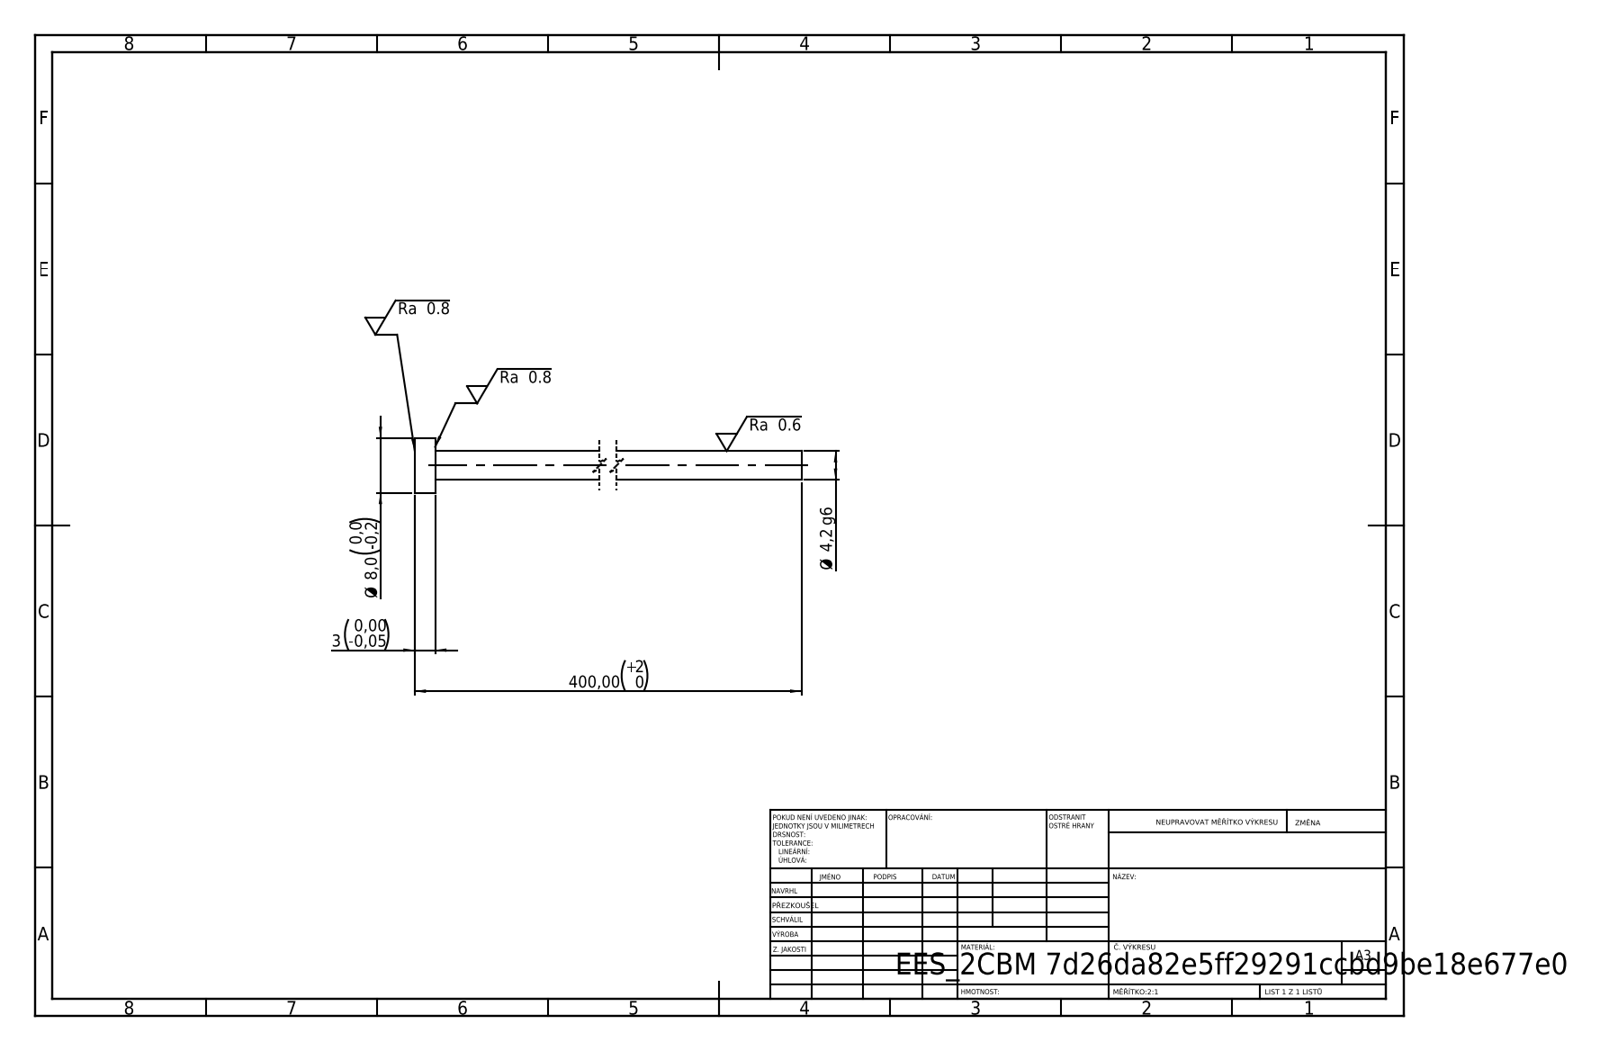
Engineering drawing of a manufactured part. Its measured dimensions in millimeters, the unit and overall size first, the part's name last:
Units: millimetres
Overall size (bounding box): 400 × 8 × 8
Round bosses / shafts (diameter × count): ⌀8 ×1, ⌀4.2 ×1
Main face-to-face distances: 3, 400, 397
Volume: 5 651 mm³ · Surface area: 5 414 mm²
Bodies: 1 solid, 7 faces (3 planar, 4 cylindrical, 0 other)
STEP written by: SolidWorks 2019 (CONFIG_CONTROL_DESIGN)
